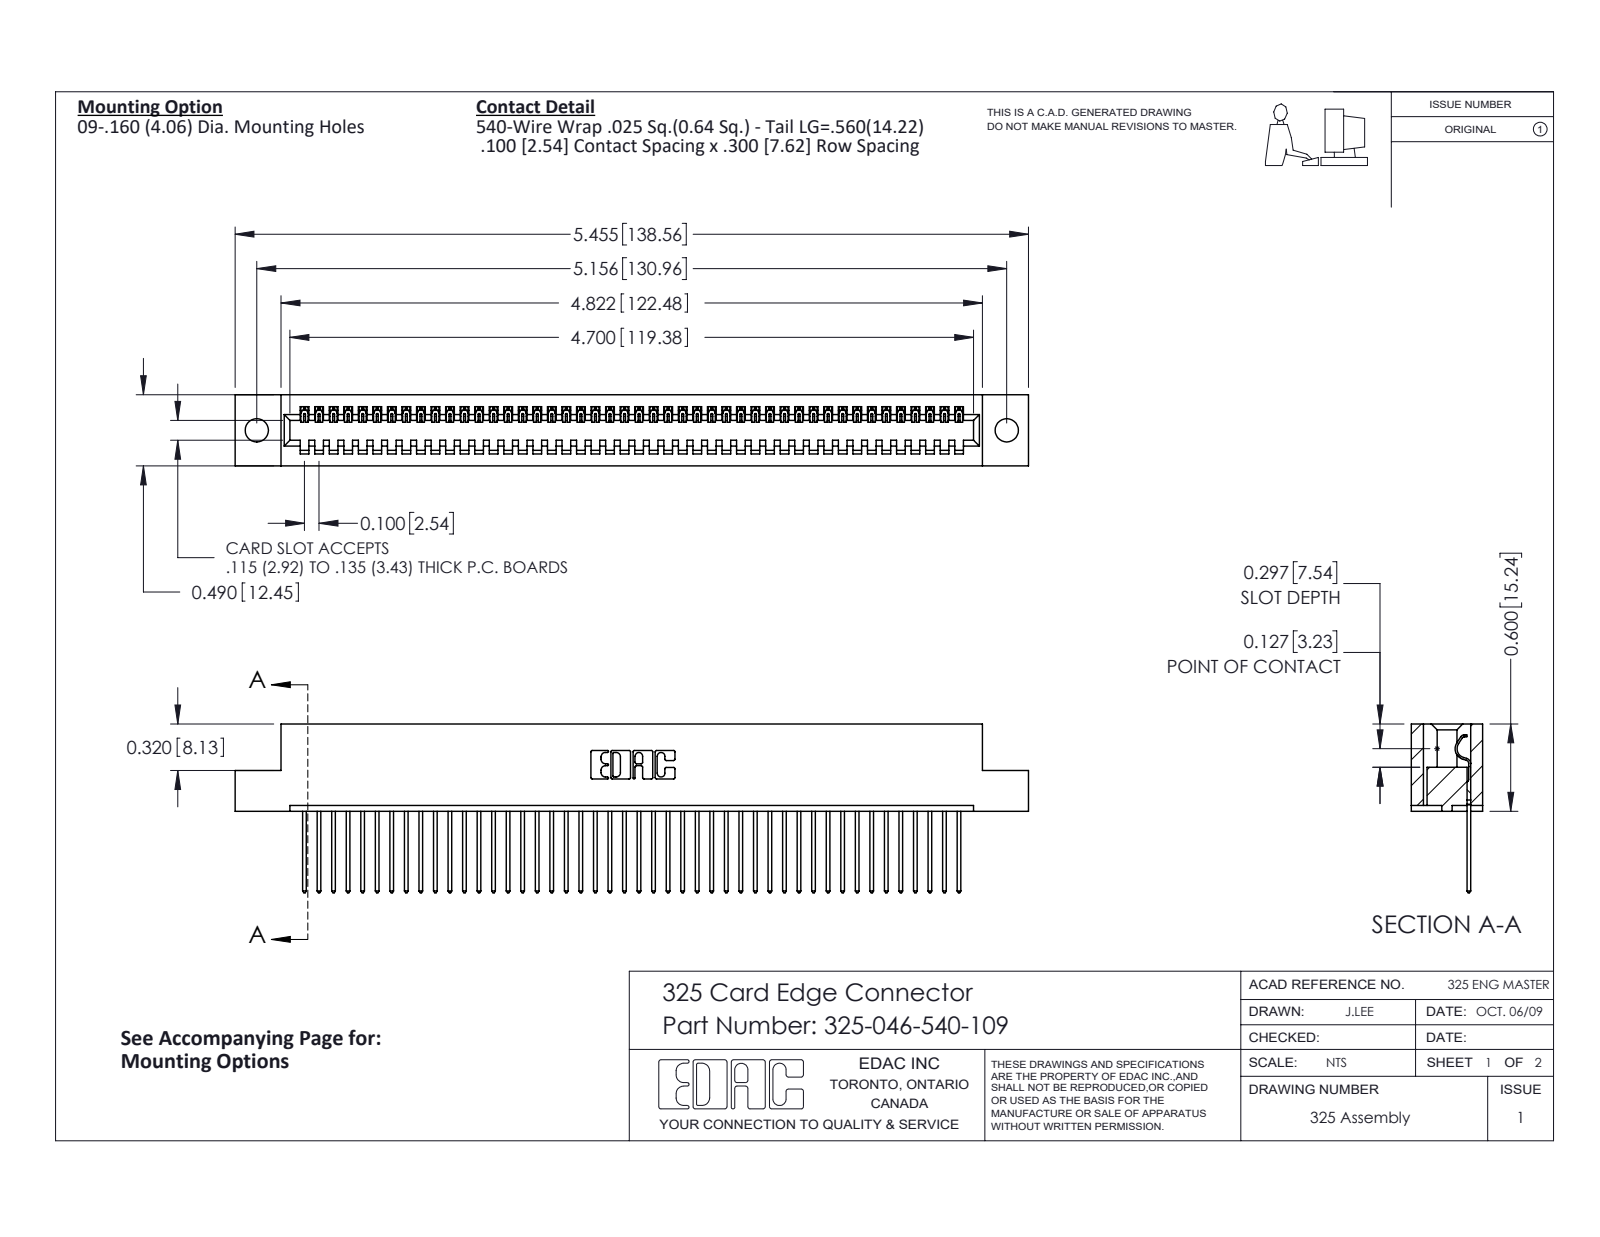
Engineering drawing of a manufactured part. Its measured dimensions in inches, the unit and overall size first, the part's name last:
Units: inches
Overall size (bounding box): 5.455 × 1.16 × 0.49
Round holes (diameter × count): ⌀0.16 ×2
Partial cylindrical surfaces — rounded edges, fillets, slot ends (radius × count): R0.006 ×92, R0.01 ×92, R0.01 ×22, R0.007 ×6, R0.031 ×6, R0.026 ×3, R0.014 ×1, R0.022 ×1
Main face-to-face distances: 0.083, 0.407, 0.49, 0.3, 0.107, 0.383, 0.025, 0.325, 0.56, 0.263
Hole centre spacings: 5.156
Volume: 1.065 in³ · Surface area: 30.21 in²
Bodies: 47 solids, 2782 faces (2002 planar, 780 cylindrical, 0 other)
Part name (STEP PRODUCT): 325-292-001_325-293-140; 325-046-540-109; 325 Part_.160 TH
STEP written by: SolidWorks 2016 (CONFIG_CONTROL_DESIGN)
